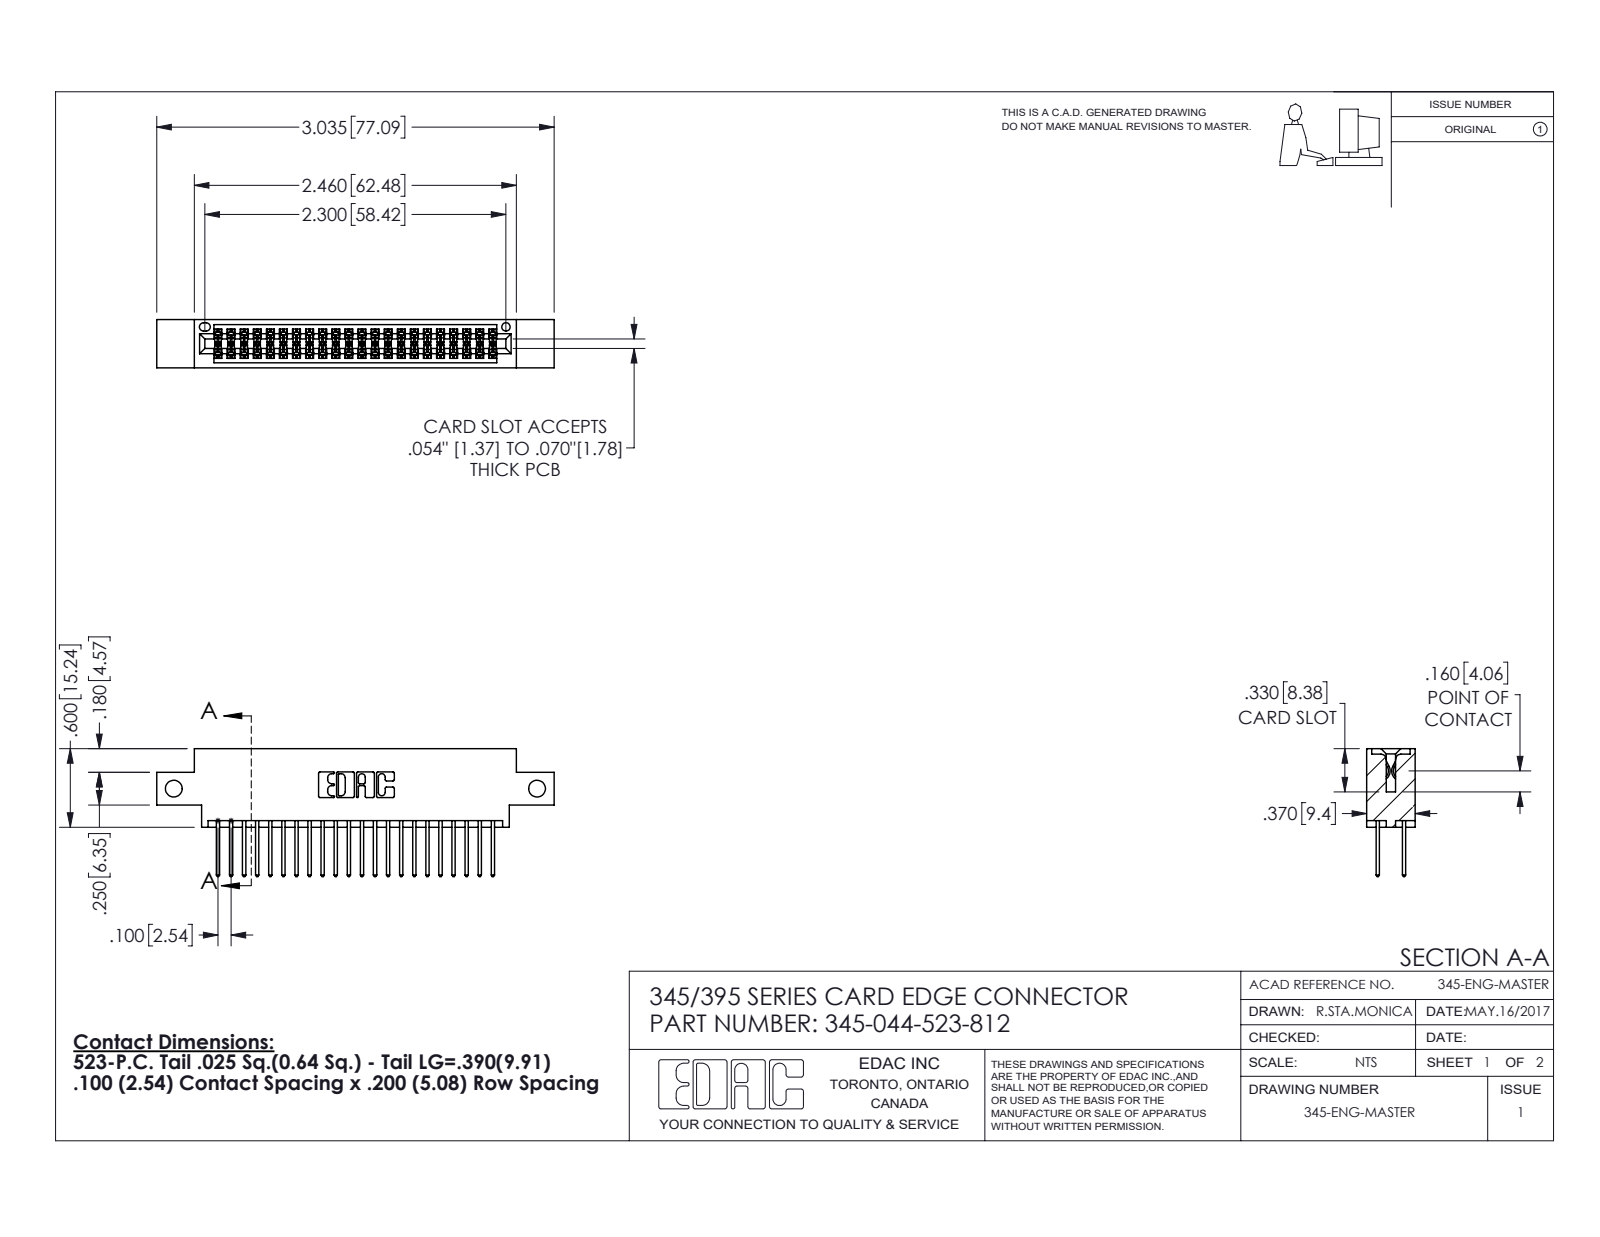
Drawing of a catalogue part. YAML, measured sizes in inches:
part_name: "345-292-001_345-293-123; 345-044-523-812; 345 Part_0.170 Offset - Side Mount"
step_written_by: "SolidWorks 2016 (CONFIG_CONTROL_DESIGN)"
units: inches
bodies: {solids: 45, faces: 2330, planar: 1536, cylindrical: 794, other: 0}
overall_size: [3.035, 0.977, 0.37]
volume: 0.439
surface_area: 16.52
round_holes:
  - {diameter: 0.128, count: 2}
  - {diameter: 0.064, count: 1}
partial_cylinders:
  - {radius: 0.006, count: 66}
  - {radius: 0.01, count: 44}
  - {radius: 0.01, count: 22}
  - {radius: 0.007, count: 6}
  - {radius: 0.031, count: 6}
  - {radius: 0.026, count: 3}
  - {radius: 0.014, count: 2}
  - {radius: 0.019, count: 2}
face_to_face_distances: [0.298, 0.072, 0.2, 0.37, 0.098, 0.272, 0.025, 0.225, 0.175, 0.15]
hole_center_spacings: [2.775]
